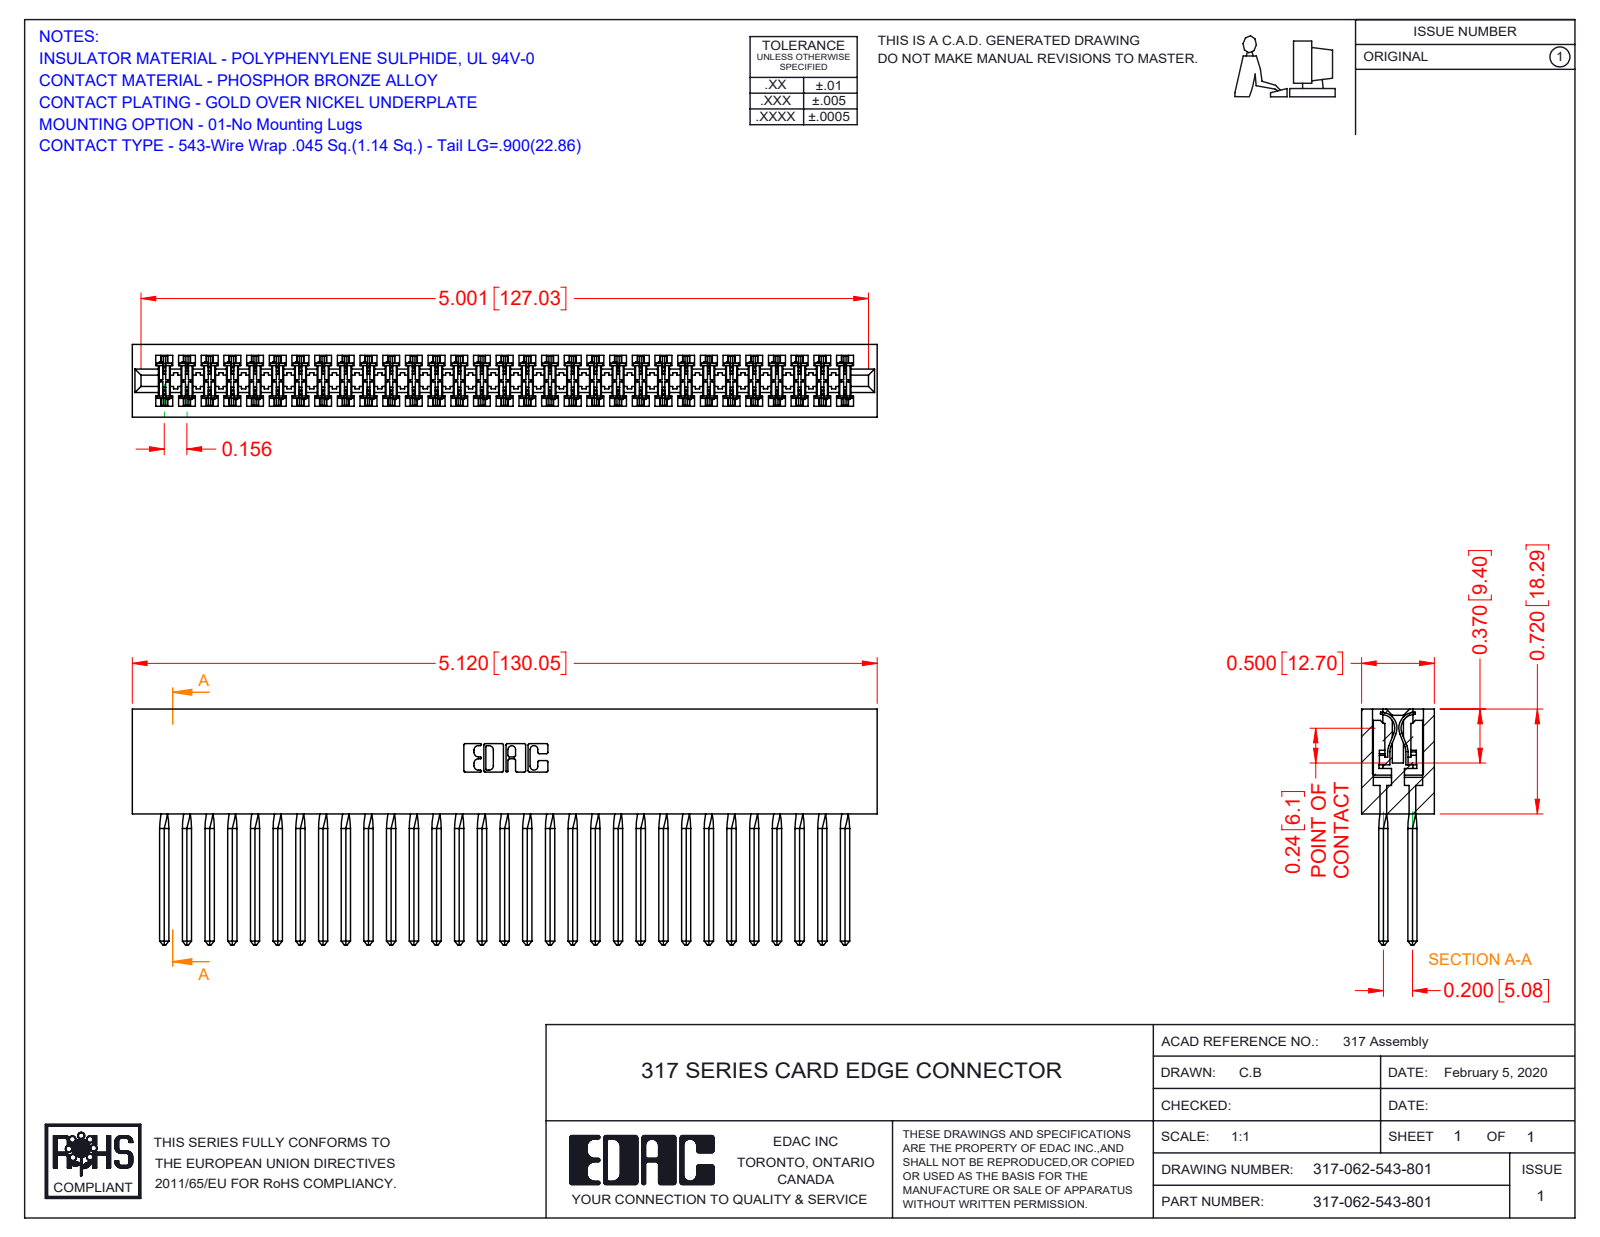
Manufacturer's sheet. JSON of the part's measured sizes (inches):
{"part_name": "317 Part_Lugless; 317-290-001_543; 317-062-543-801", "step_written_by": "SolidWorks 2016 (CONFIG_CONTROL_DESIGN)", "units": "inches", "bodies": {"solids": 63, "faces": 5608, "planar": 4576, "cylindrical": 784, "other": 248}, "overall_size": [5.12, 1.62, 0.5], "volume_in3": 1.437, "surface_area_in2": 55.15, "partial_cylinders_radius": [[0.015, 124], [0.01, 22], [0.007, 6], [0.031, 6], [0.026, 3], [0.095, 2], [0.1, 2], [0.11, 2]], "face_to_face_distances": [0.075, 0.5, 0.425, 0.35, 0.11, 0.195, 0.094, 0.2, 0.115, 0.131]}
